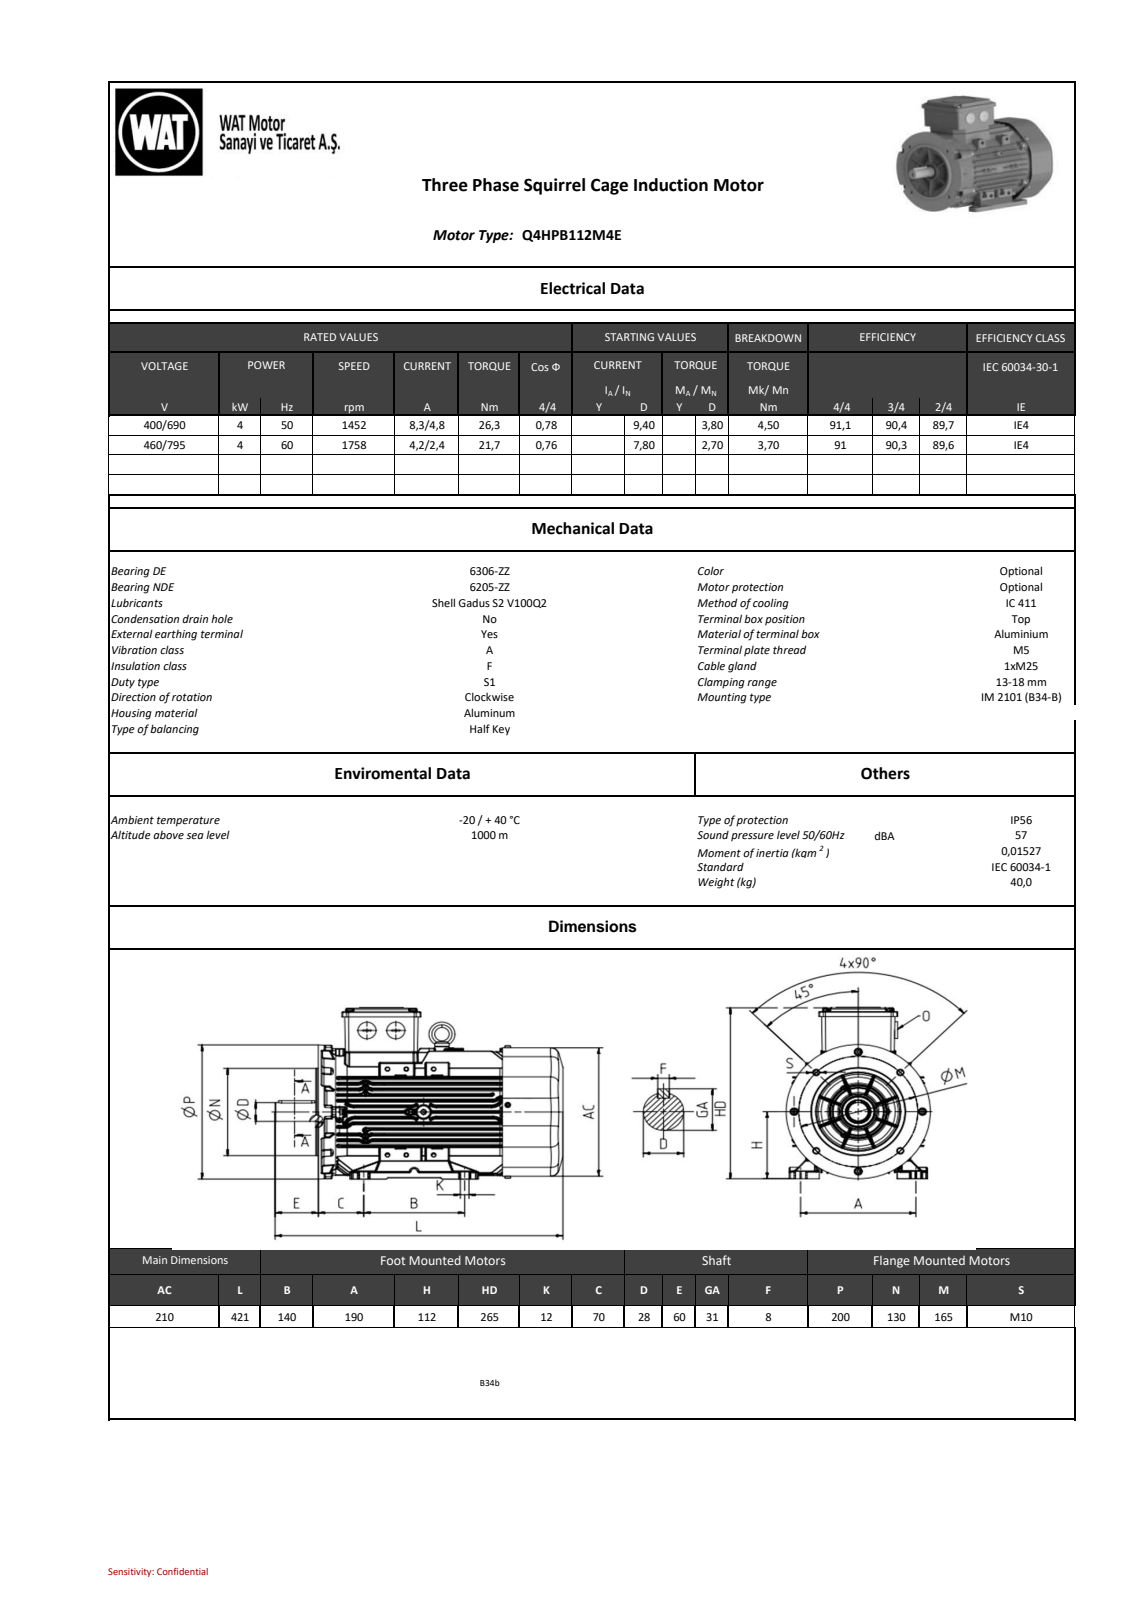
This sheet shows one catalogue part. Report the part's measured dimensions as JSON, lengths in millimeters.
{"part_name": "QH series_ 112_B34b _DEEP COVER__stp_objects", "step_written_by": "SIEMENS PLM Software NX2206.8101 (AUTOMOTIVE_DESIGN)", "units": "millimeters", "bodies": {"solids": 0, "faces": 7597, "planar": 1691, "cylindrical": 2927, "other": 2979}, "overall_size": [421, 275.46, 225.11], "round_holes": [[3.5, 2], [4.6, 2], [8, 1], [8.5, 1], [47, 1], [78, 1]], "round_bosses_or_shafts": [[8, 8], [13, 4], [25, 2], [188, 1], [130, 1], [35.83, 1], [30, 1], [29.5, 1]], "partial_cylinders_radius": [[2, 731], [0.8, 608], [1, 435], [0.5, 276], [3, 70], [4, 12], [6, 12], [10, 10]], "face_to_face_distances": [1, 21.5, 10.99, 35.96, 99.54, 24.97, 8.16, 112.88, 89.87, 90.43]}
